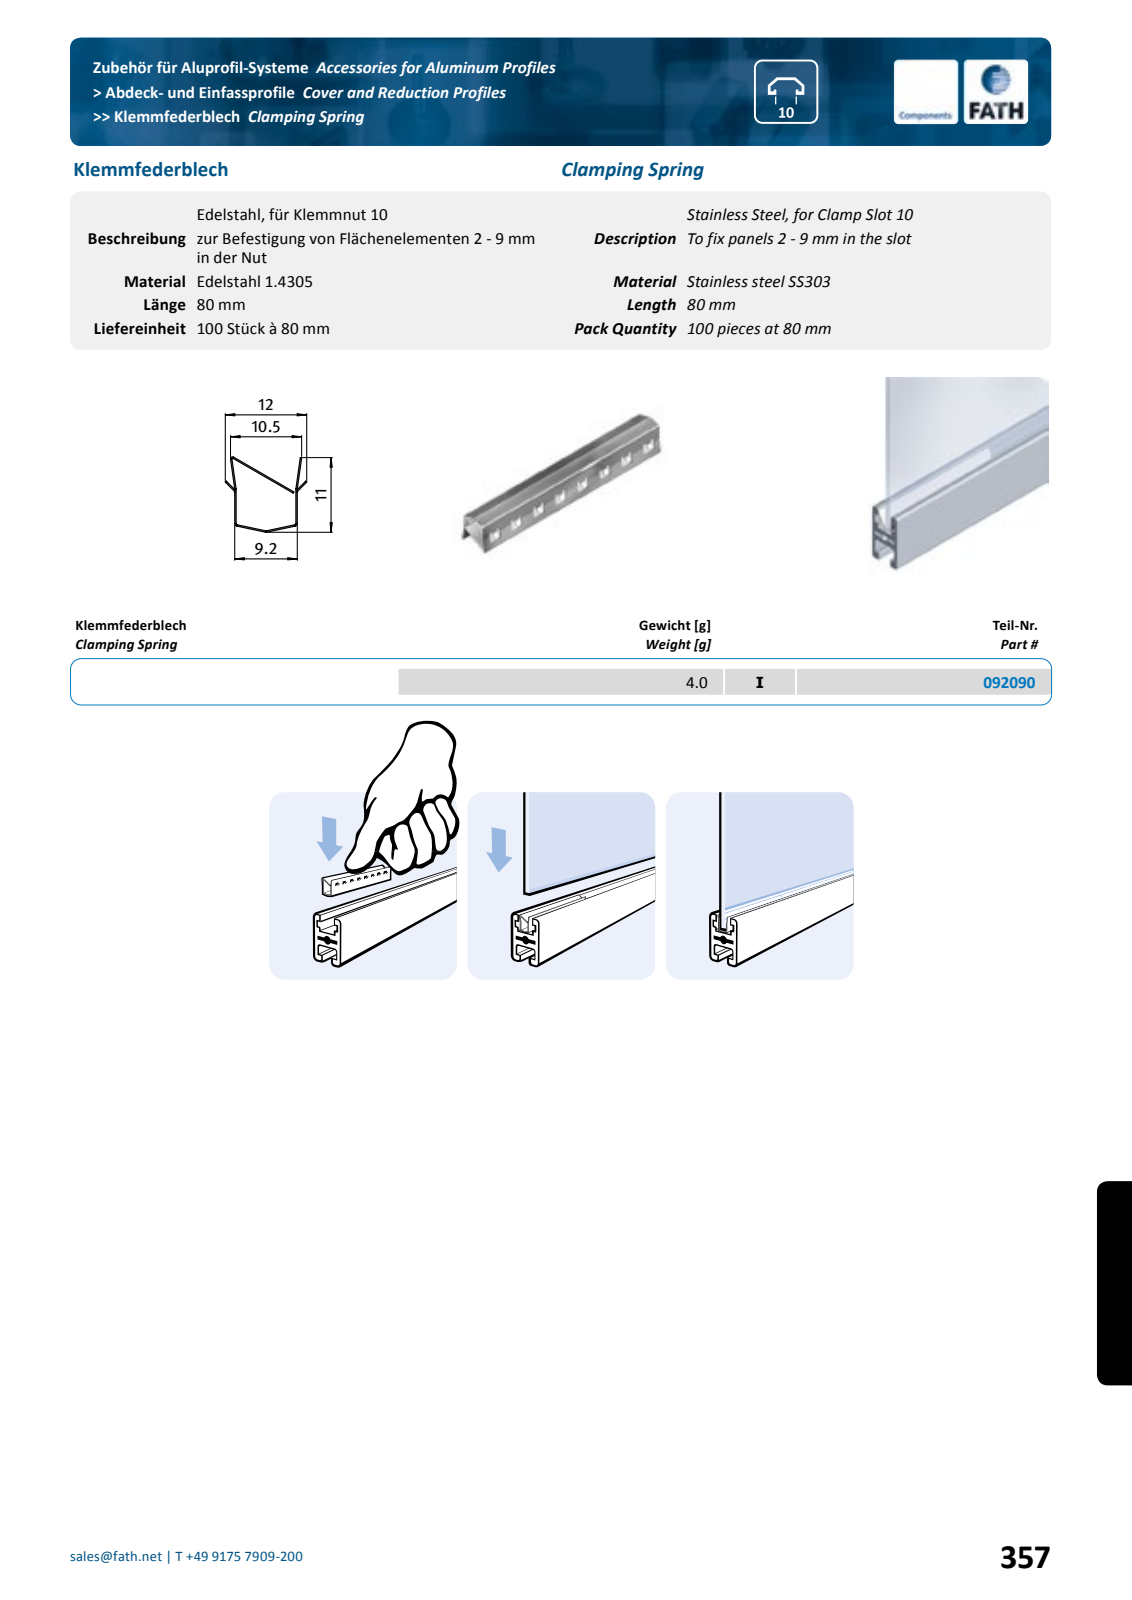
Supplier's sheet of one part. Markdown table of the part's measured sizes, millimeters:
| quantity | value |
| --- | --- |
| part name | fath_092090 |
| STEP written by | Spatial InterOp 3D (automotive_design) |
| units | millimeters |
| bodies | 1 solid, 284 faces (146 planar, 138 cylindrical, 0 other) |
| overall size | 80 × 12 × 11.11 |
| volume | 594 mm³ |
| surface area | 6 053 mm² |
| partial cylindrical surfaces (radius × count) | 0.1 × 33, 0.5 × 16, 0.65 × 16, 0.2 × 5, 0.4 × 5, 0.3 × 1 |
| main face-to-face distances | 9, 8.8, 9.2, 10, 20, 30, 4.6, 40, 14.6, 5.4 |
